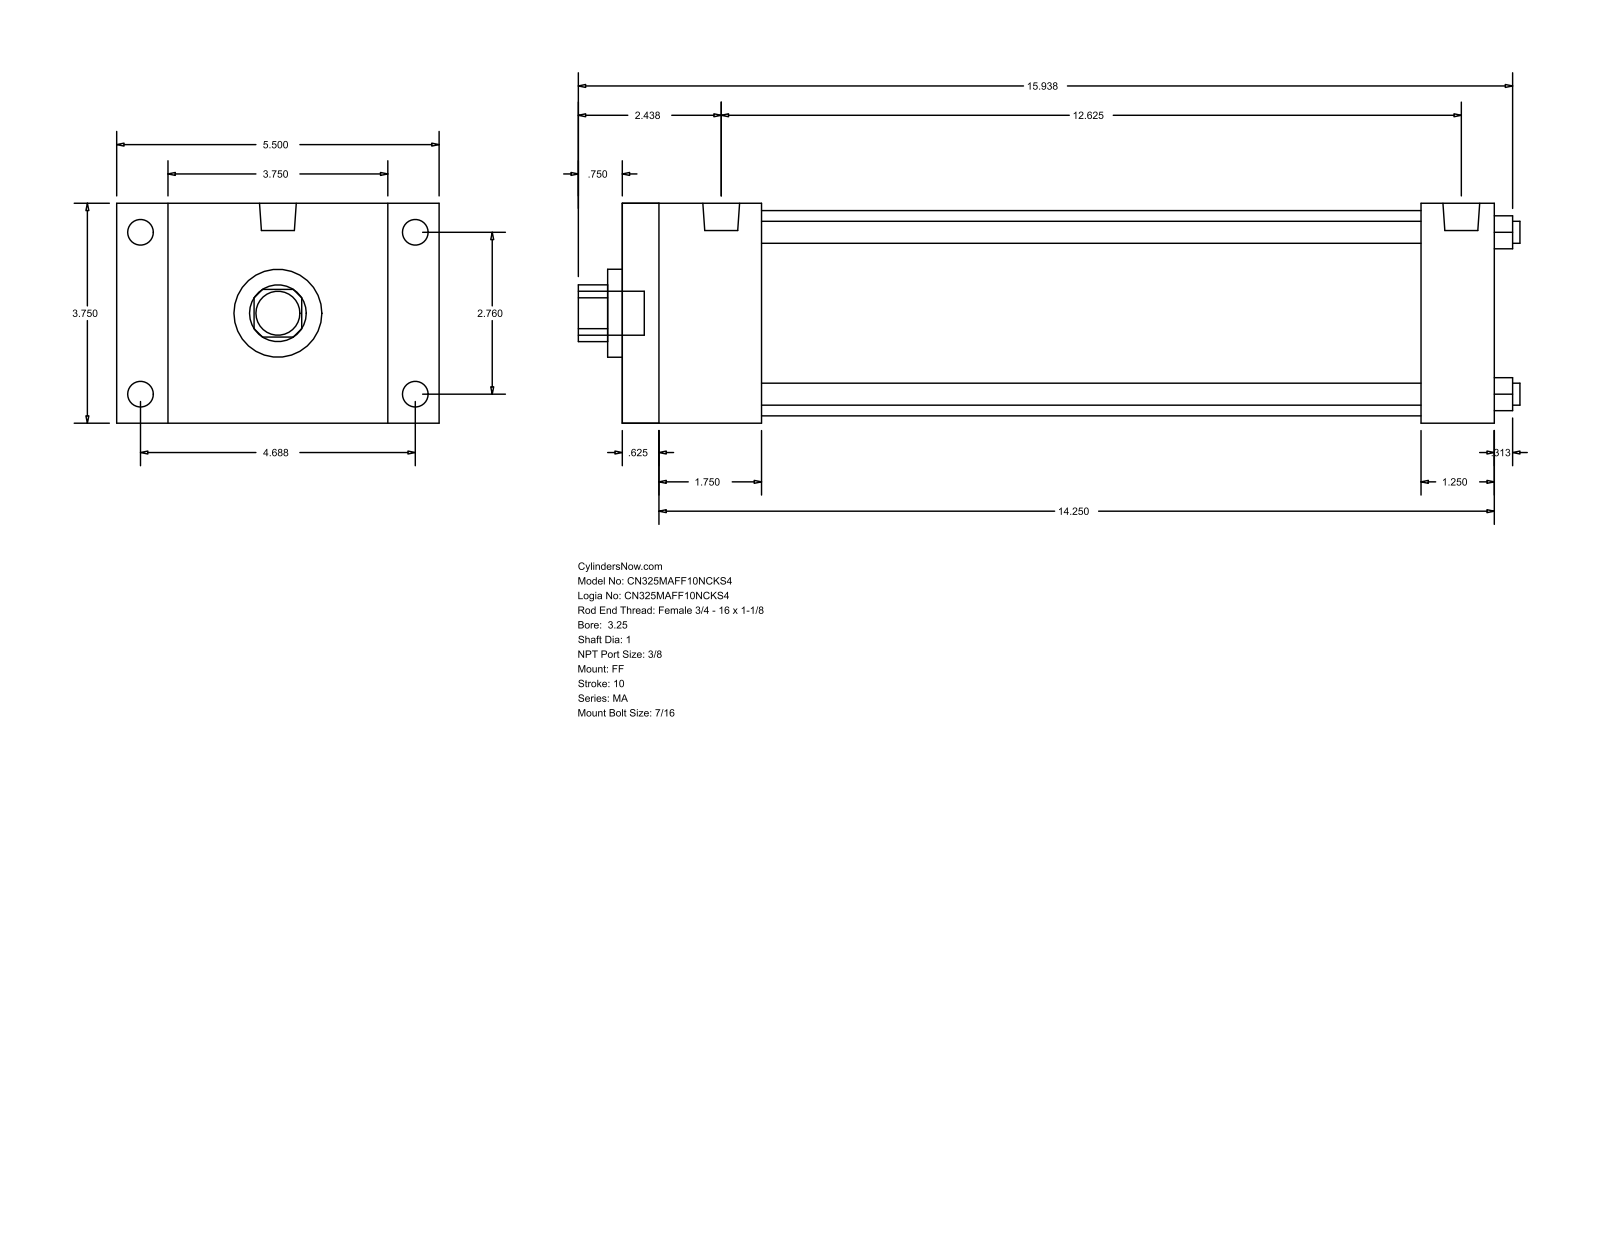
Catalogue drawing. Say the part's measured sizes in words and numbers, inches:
The part is named "MA_FF__0325_1". Its 3-D file was written by "GSSL Pune (CONFIG_CONTROL_DESIGN)". It is 0 solids with 92 faces: 64 planar, 28 cylindrical and 0 other. Overall it measures 16.063 by 5.5 by 3.75 inches. Round holes: 4 of diameter 0.375, 1 of diameter 1, 1 of diameter 1.5, 1 of diameter 3.5. Round bosses or shafts: 8 of diameter 0.437, 2 of diameter 0.627, 1 of diameter 0.75. Partial cylindrical surfaces (rounded edges, fillets, slot ends): 1 of radius 0.484. The main face-to-face distances are 3.75, 14.875, 0.625, 14.25, 0.875, 4.625, 2.375, 13.625, 1.75, 13. The hole center spacings are 1.952, 2.76, 3.903.
